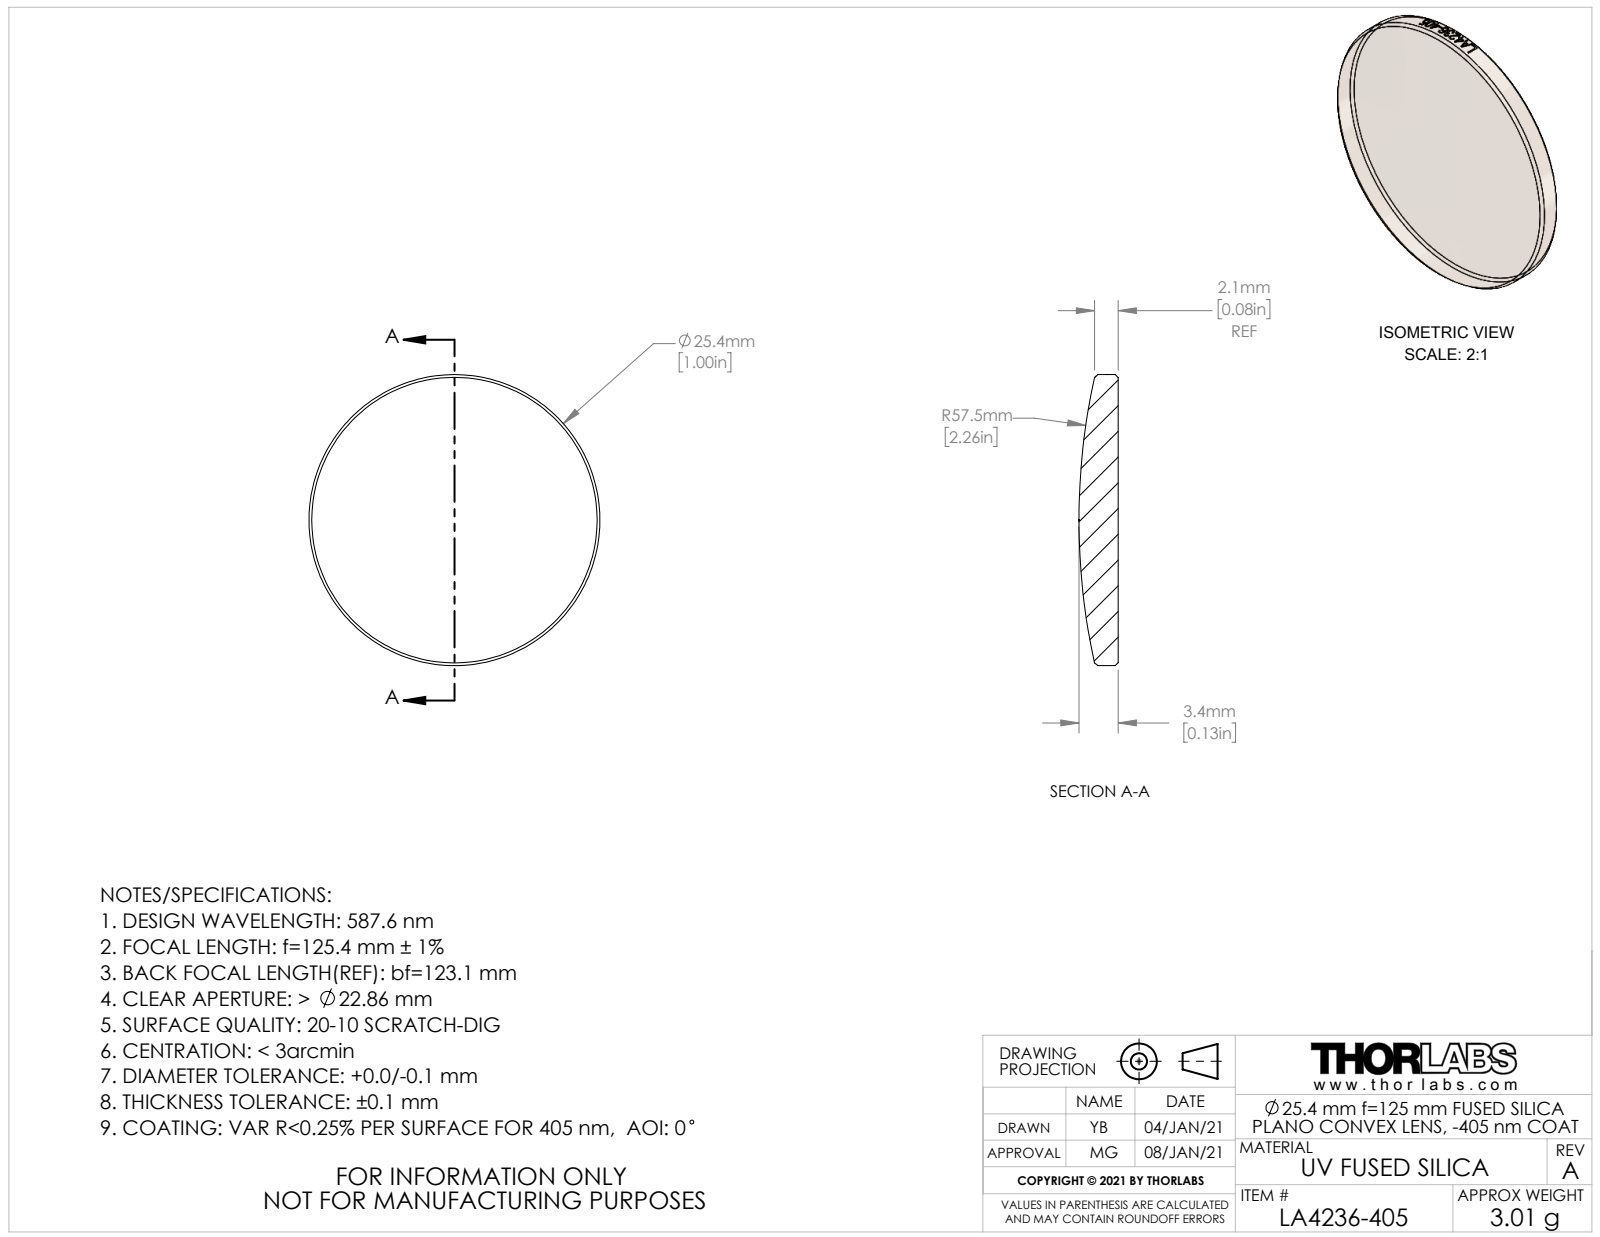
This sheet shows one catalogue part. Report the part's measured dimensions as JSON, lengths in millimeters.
{"part_name": "CTN016822-E0W; CTN016842", "step_written_by": "SolidWorks 2018 (AUTOMOTIVE_DESIGN)", "units": "millimeters", "bodies": {"solids": 1, "faces": 30, "planar": 1, "cylindrical": 23, "other": 6}, "overall_size": [25.4, 25.4, 3.4], "volume_mm3": 1400, "surface_area_mm2": 1159, "round_bosses_or_shafts": [[25.4, 1]]}
